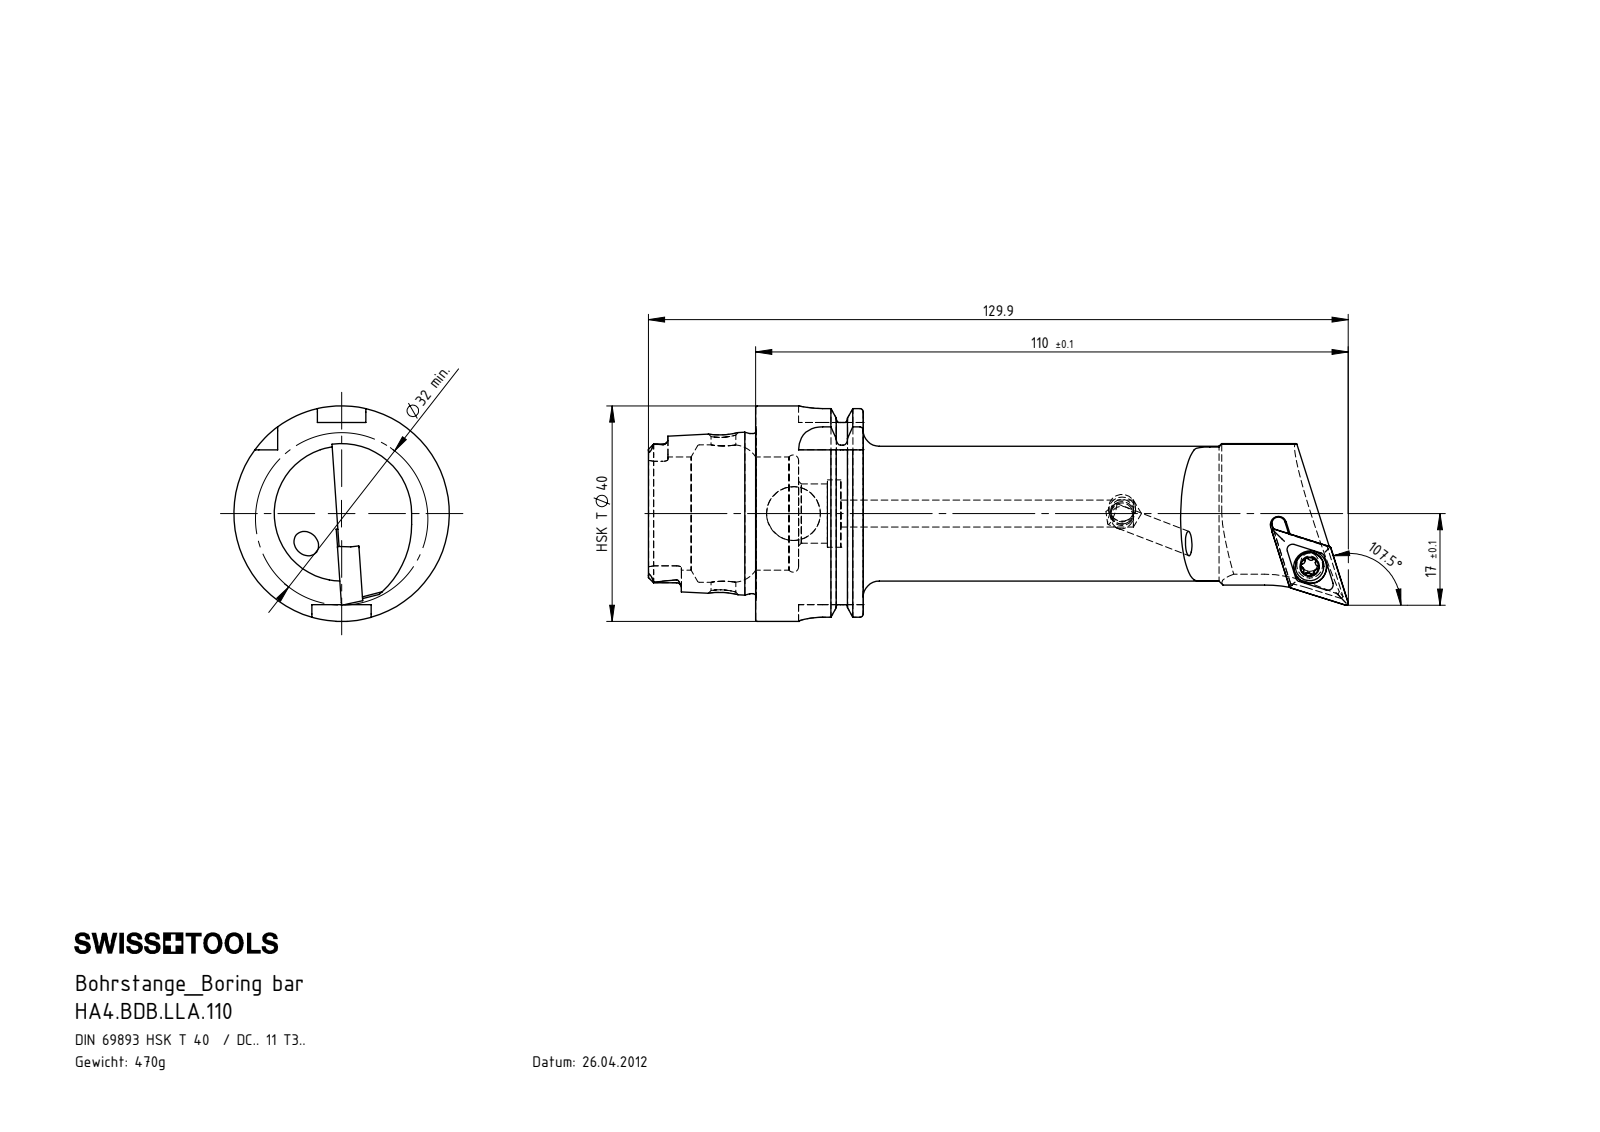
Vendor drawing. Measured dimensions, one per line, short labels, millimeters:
name: HA4-BDB.LLA.110_A; DCMT11T304; WCB-ER2.001.009_A; KVT_MB_600_050 (+1 more)
written by: SolidWorks 2017 (AUTOMOTIVE_DESIGN)
unit: mm
bodies: 5 solids, 309 faces (77 planar, 92 cylindrical, 140 other)
size: 129.9 × 40 × 40
volume: 59 641 mm³; area: 17 960 mm²
holes: 2× ⌀4.2, 1× ⌀3.3, 1× ⌀4, 1× ⌀4.4, 1× ⌀4.6, 1× ⌀5, 1× ⌀6.1, 1× ⌀10, 1× ⌀11, 1× ⌀12.5, 1× ⌀21, 1× ⌀25.5
bosses: 1× ⌀40, 1× ⌀34.75, 1× ⌀29.71, 1× ⌀25, 1× ⌀5.25, 1× ⌀5, 1× ⌀4
rounds: 6× R0.34, 6× R0.59, 6× R0.9, 4× R4.5, 2× R1.82, 2× R1.88, 1× R1.25, 1× R3
face distances: 19.95, 7.95, 12, 3.67, 19.9, 27.85, 39.85, 35.7, 15.8, 7.85
